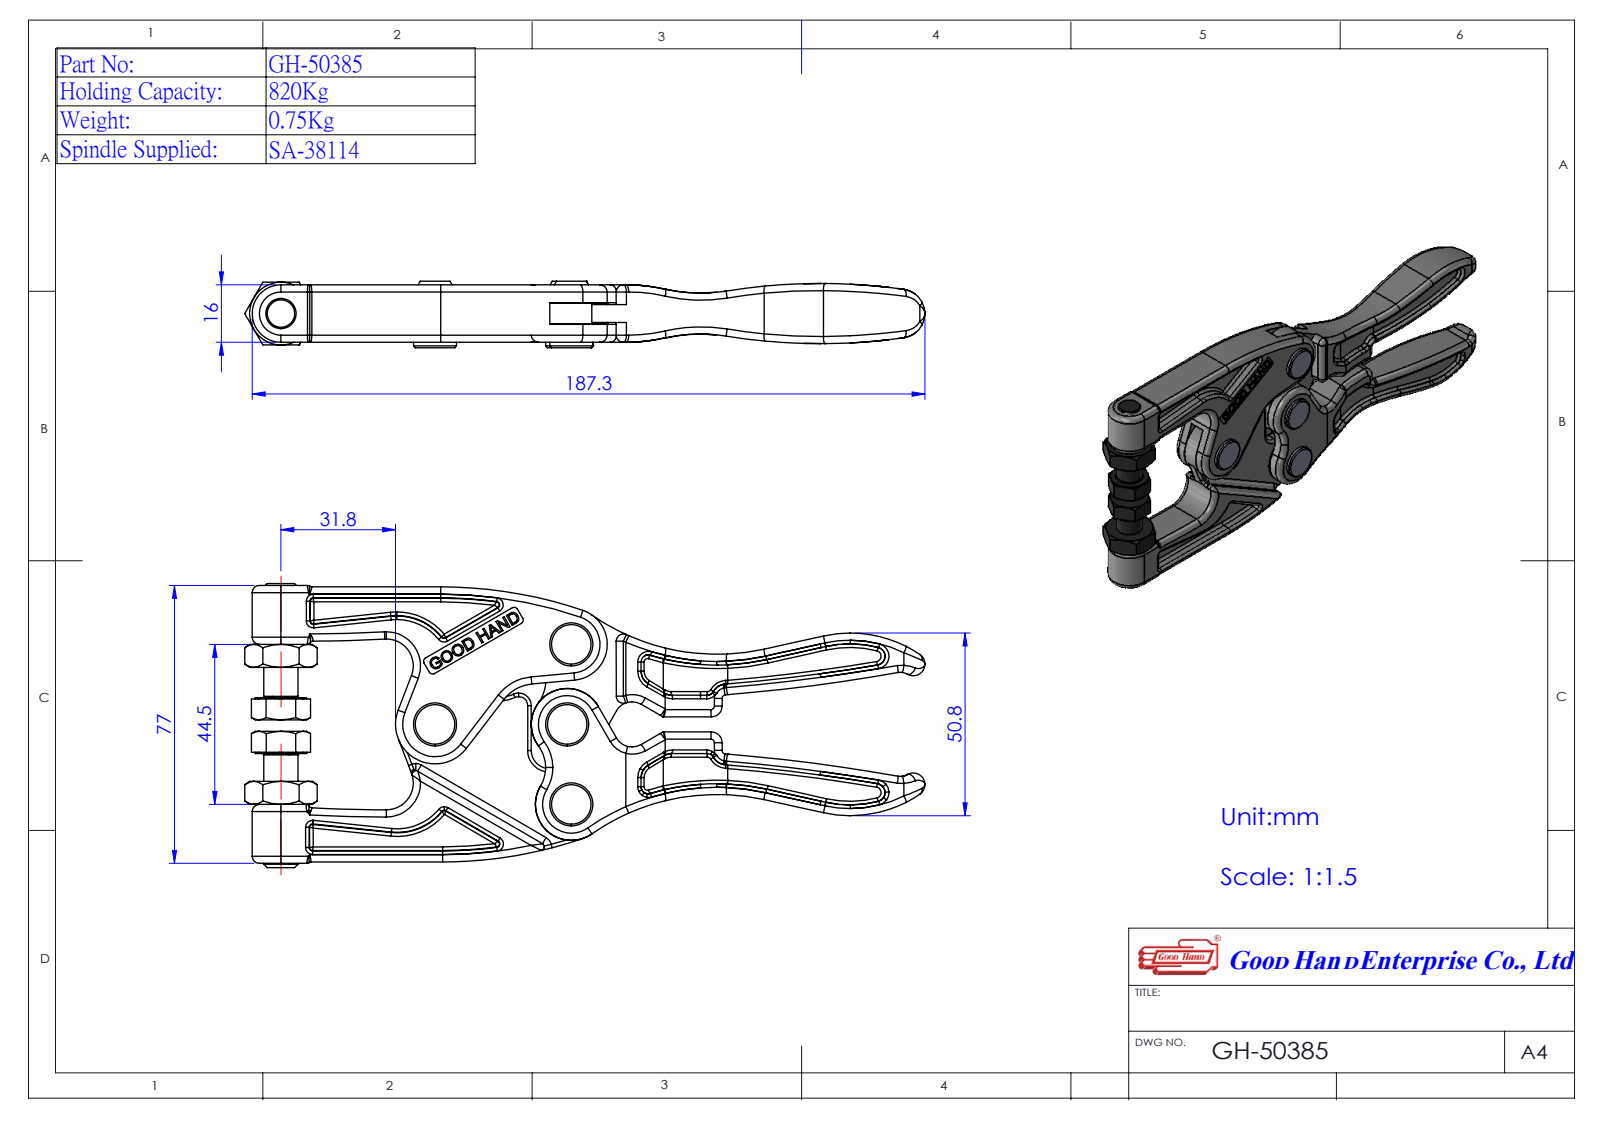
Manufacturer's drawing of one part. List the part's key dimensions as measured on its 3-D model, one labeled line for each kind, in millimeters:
Part name (STEP PRODUCT): Group3^GH-50385(簡化); GH-50385(簡化); Hex Bolt_AI-1^GH-50385(簡化); 35038501-1^GH-50385(簡化) (+3 more)
STEP written by: SolidWorks 2016 (AUTOMOTIVE_DESIGN)
Units: millimetres
Bodies: 9 solids, 765 faces (250 planar, 208 cylindrical, 307 other)
Overall size (bounding box): 189.1 × 77.34 × 19.57
Volume: 99 280 mm³ · Surface area: 49 779 mm²
Round holes (diameter × count): ⌀8 ×4, ⌀8.5 ×2, ⌀8.43 ×1, ⌀10 ×1
Round bosses / shafts (diameter × count): ⌀12 ×4, ⌀10.5 ×4, ⌀20 ×3, ⌀9.53 ×2
Partial cylindrical surfaces — rounded edges, fillets, slot ends (radius × count): R2 ×24, R10 ×7, R1 ×6, R5 ×3, R11 ×3, R3 ×2, R3.25 ×2, R6.8 ×2
Main face-to-face distances: 5, 11, 6, 4.92, 16, 5.08, 11.08, 10.92, 6.08, 5.92
Hole centre spacings: 22.3, 44, 36.79, 44.54
